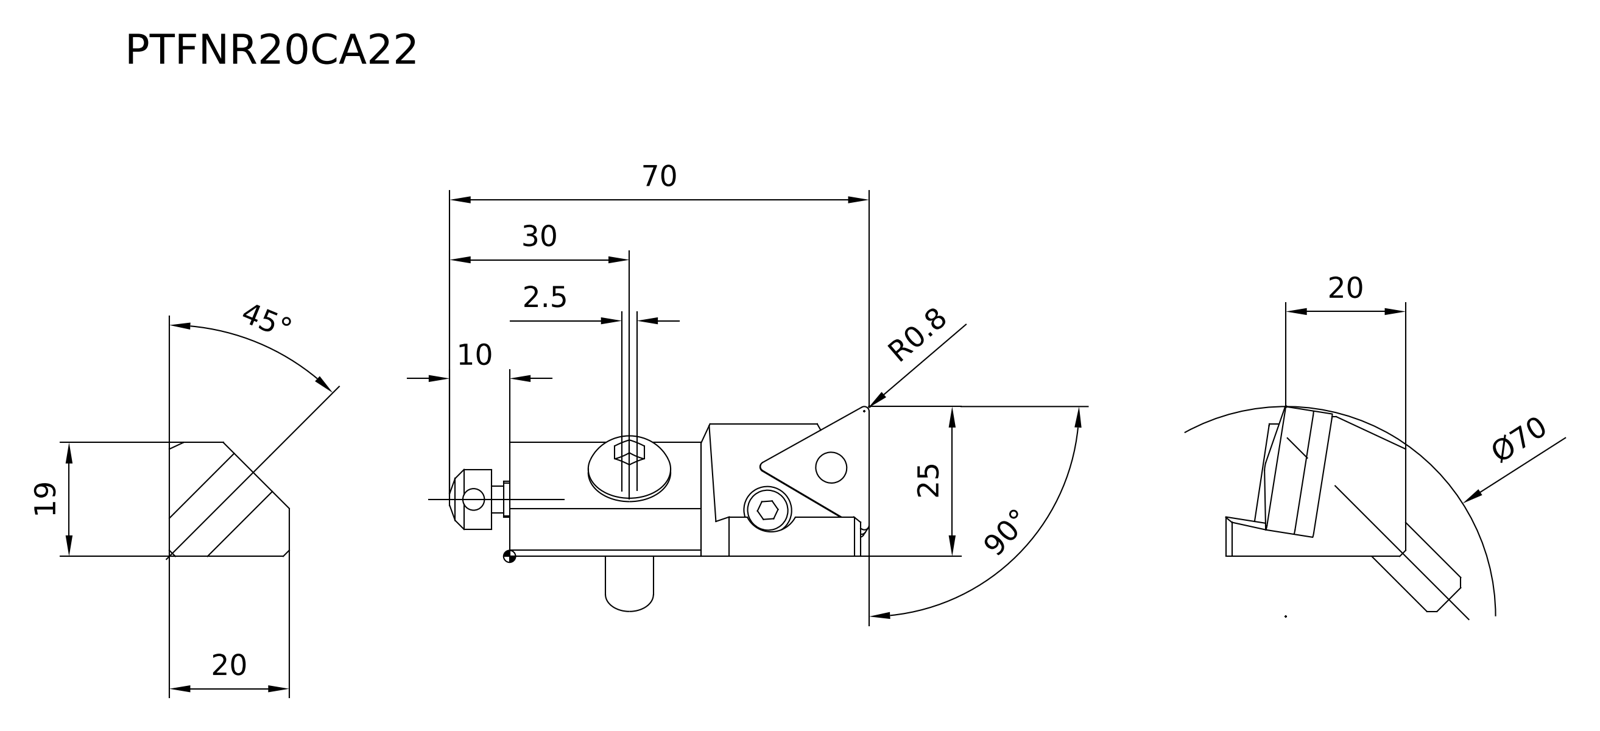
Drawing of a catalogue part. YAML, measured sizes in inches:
part_name: "PTFNR20CA22_ASM"
step_written_by: "SIEMENS PLM Software NX 10.0 (AUTOMOTIVE_DESIGN)"
units: inches
bodies: {solids: 8, faces: 215, planar: 94, cylindrical: 62, other: 59}
overall_size: [2.737, 1.543, 1.317]
volume: 1.374
surface_area: 16.87
round_holes:
  - {diameter: 0.142, count: 2}
  - {diameter: 0.197, count: 2}
  - {diameter: 0.256, count: 1}
  - {diameter: 0.268, count: 1}
round_bosses_or_shafts:
  - {diameter: 0.315, count: 3}
  - {diameter: 0.236, count: 2}
  - {diameter: 0.541, count: 1}
  - {diameter: 0.394, count: 1}
  - {diameter: 0.256, count: 1}
  - {diameter: 0.177, count: 1}
  - {diameter: 0.142, count: 1}
partial_cylinders:
  - {radius: 0.012, count: 4}
  - {radius: 0.177, count: 3}
  - {radius: 0.028, count: 2}
  - {radius: 0.276, count: 2}
  - {radius: 0.016, count: 1}
  - {radius: 0.031, count: 1}
  - {radius: 0.047, count: 1}
  - {radius: 0.087, count: 1}
face_to_face_distances: [2.306, 0.87, 0.787, 0.122, 0.748, 0.293, 0.168, 0.125, 0.394, 1.181]
hole_center_spacings: [0.506, 2.335]
